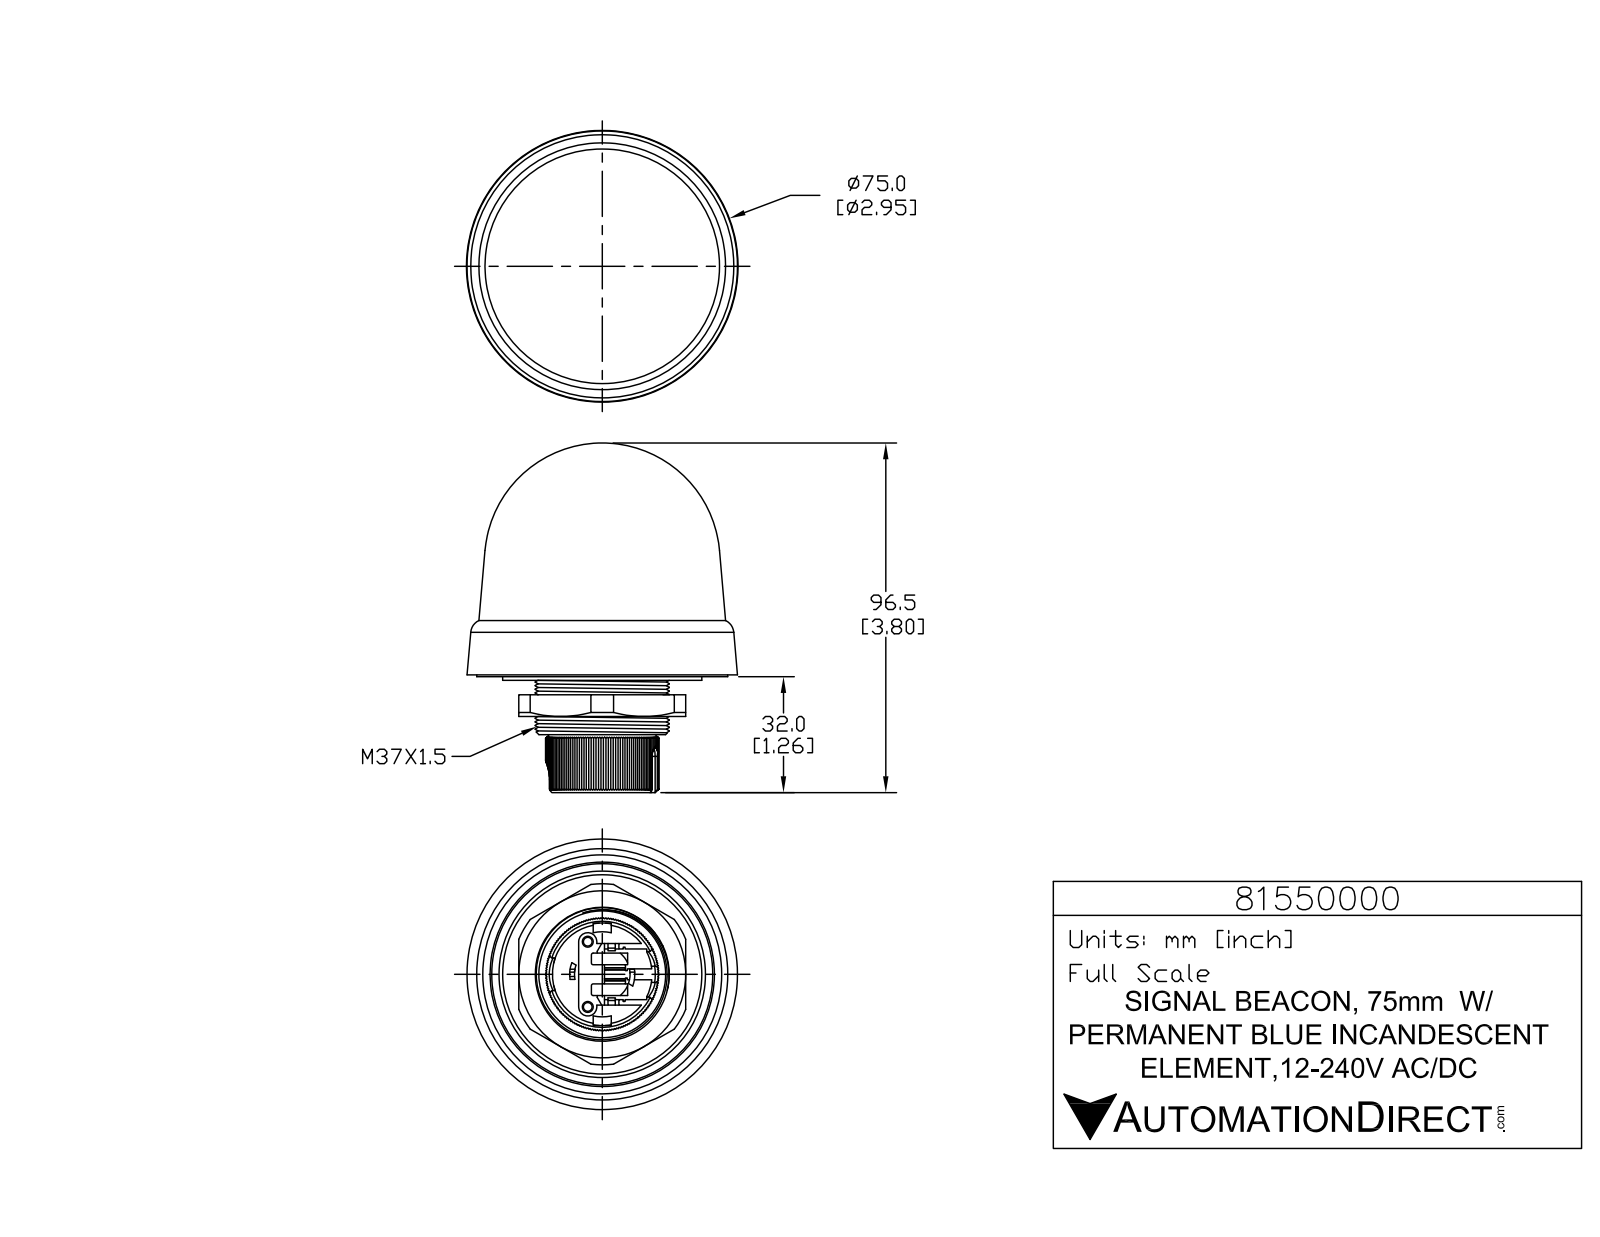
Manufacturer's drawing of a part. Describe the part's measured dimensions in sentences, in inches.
The part is named "81550000". Its 3-D file was written by "SolidWorks 2019 (CONFIG_CONTROL_DESIGN)". It is 3 solids with 560 faces: 432 planar, 80 cylindrical and 48 other. Overall it measures 3.799 by 2.941 by 2.941 inches. Its volume is 12.36 cubic inches and its surface area 58.68 square inches. Round holes: 2 of diameter 0.094, 2 of diameter 0.118, 1 of diameter 0.604, 1 of diameter 1.142. Round bosses or shafts: 2 of diameter 0.217, 2 of diameter 0.067, 1 of diameter 2.165, 1 of diameter 1.457, 1 of diameter 0.925. Partial cylindrical surfaces (rounded edges, fillets, slot ends): 6 of radius 0.008, 6 of radius 0.039, 4 of radius 0.02, 2 of radius 0.031, 2 of radius 0.079, 2 of radius 0.098, 1 of radius 0.177, 1 of radius 0.354. The main face-to-face distances are 0.177, 0.354, 0.197, 0.433, 0.512, 0.335, 0.059, 0.394, 0.118, 0.157. The hole center spacings are 0.388, 0.709.
